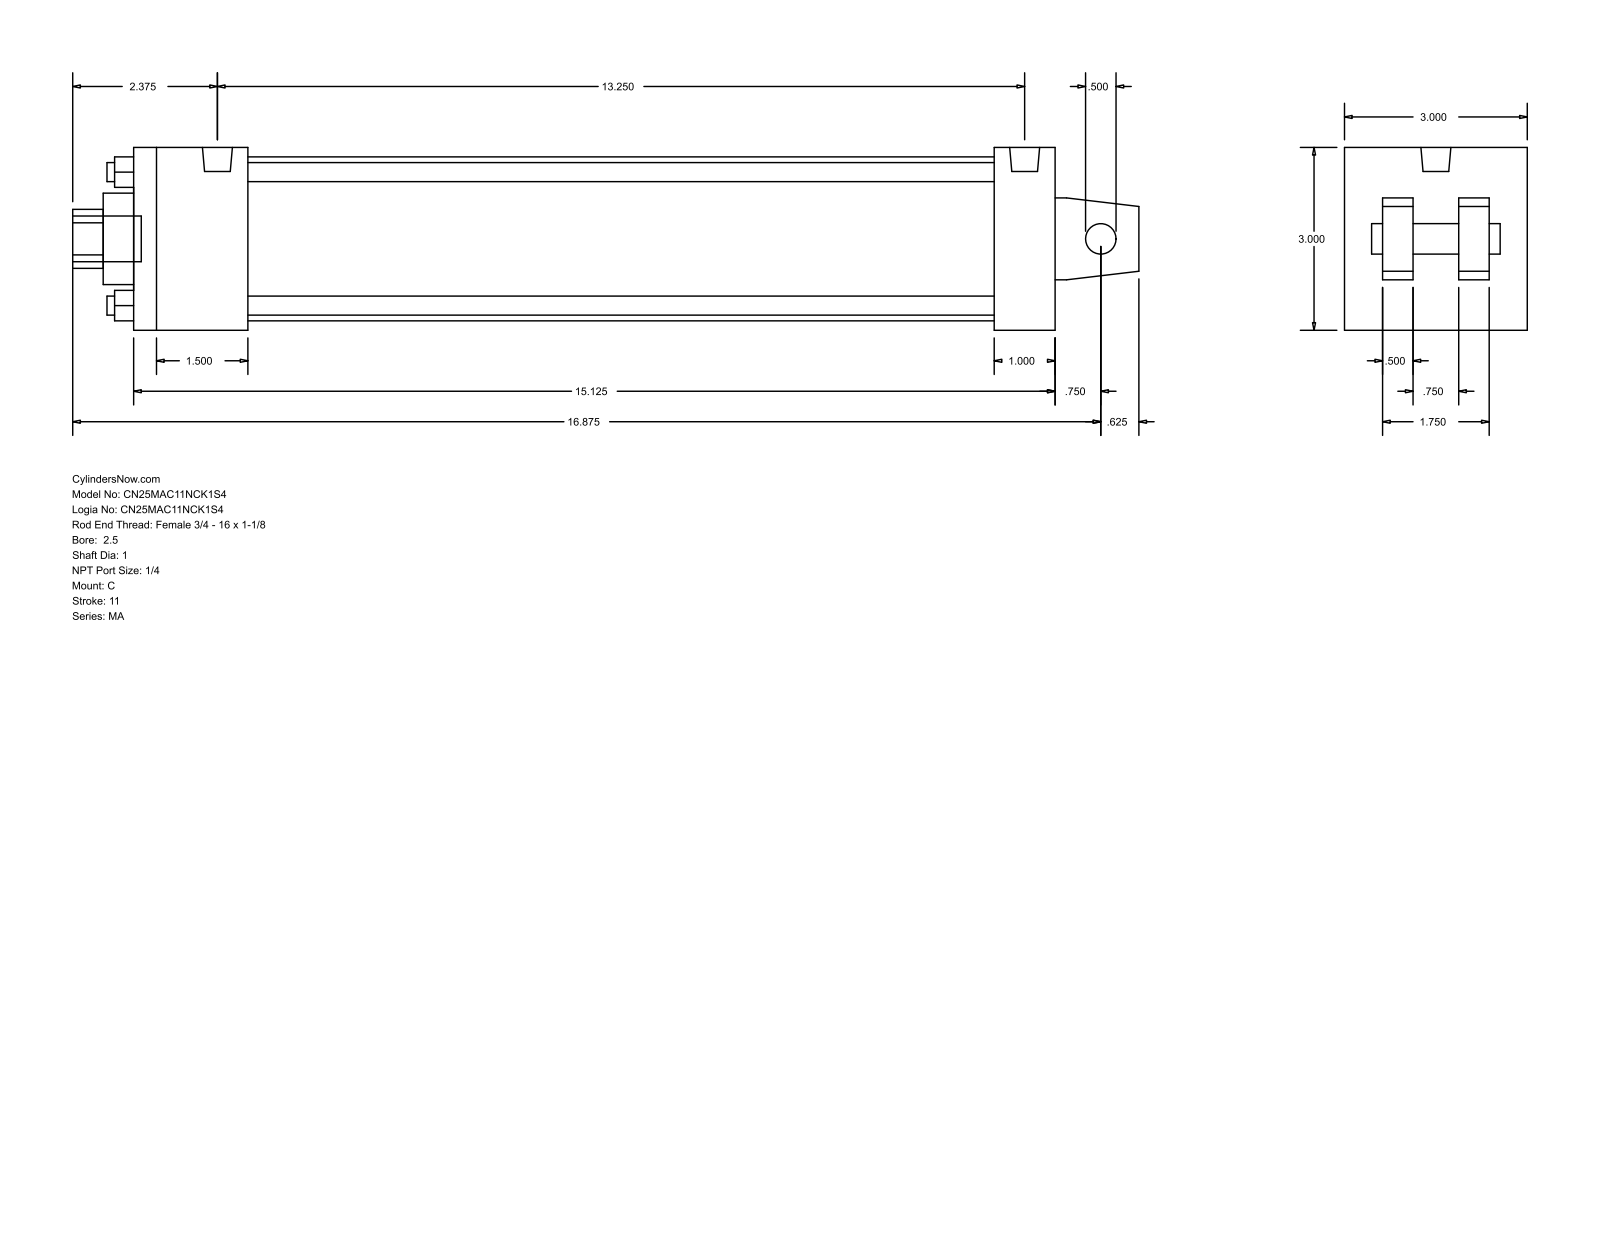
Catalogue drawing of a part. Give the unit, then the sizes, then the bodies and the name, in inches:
Units: inches
Overall size (bounding box): 17.5 × 3 × 3
Round holes (diameter × count): ⌀0.313 ×4, ⌀0.5 ×1, ⌀1 ×1, ⌀1.5 ×1, ⌀2.69 ×1
Round bosses / shafts (diameter × count): ⌀0.313 ×4, ⌀0.492 ×2, ⌀0.75 ×1
Partial cylindrical surfaces — rounded edges, fillets, slot ends (radius × count): R0.484 ×1
Main face-to-face distances: 3, 1.875, 15.125, 0.5, 0.625, 2.375, 1.125, 14.125, 12.25, 13.25
Hole centre spacings: 1.548, 2.19, 3.097
Bodies: 0 solids, 103 faces (76 planar, 27 cylindrical, 0 other)
Part name (STEP PRODUCT): MA_C__0250_1
STEP written by: GSSL Pune (CONFIG_CONTROL_DESIGN)
